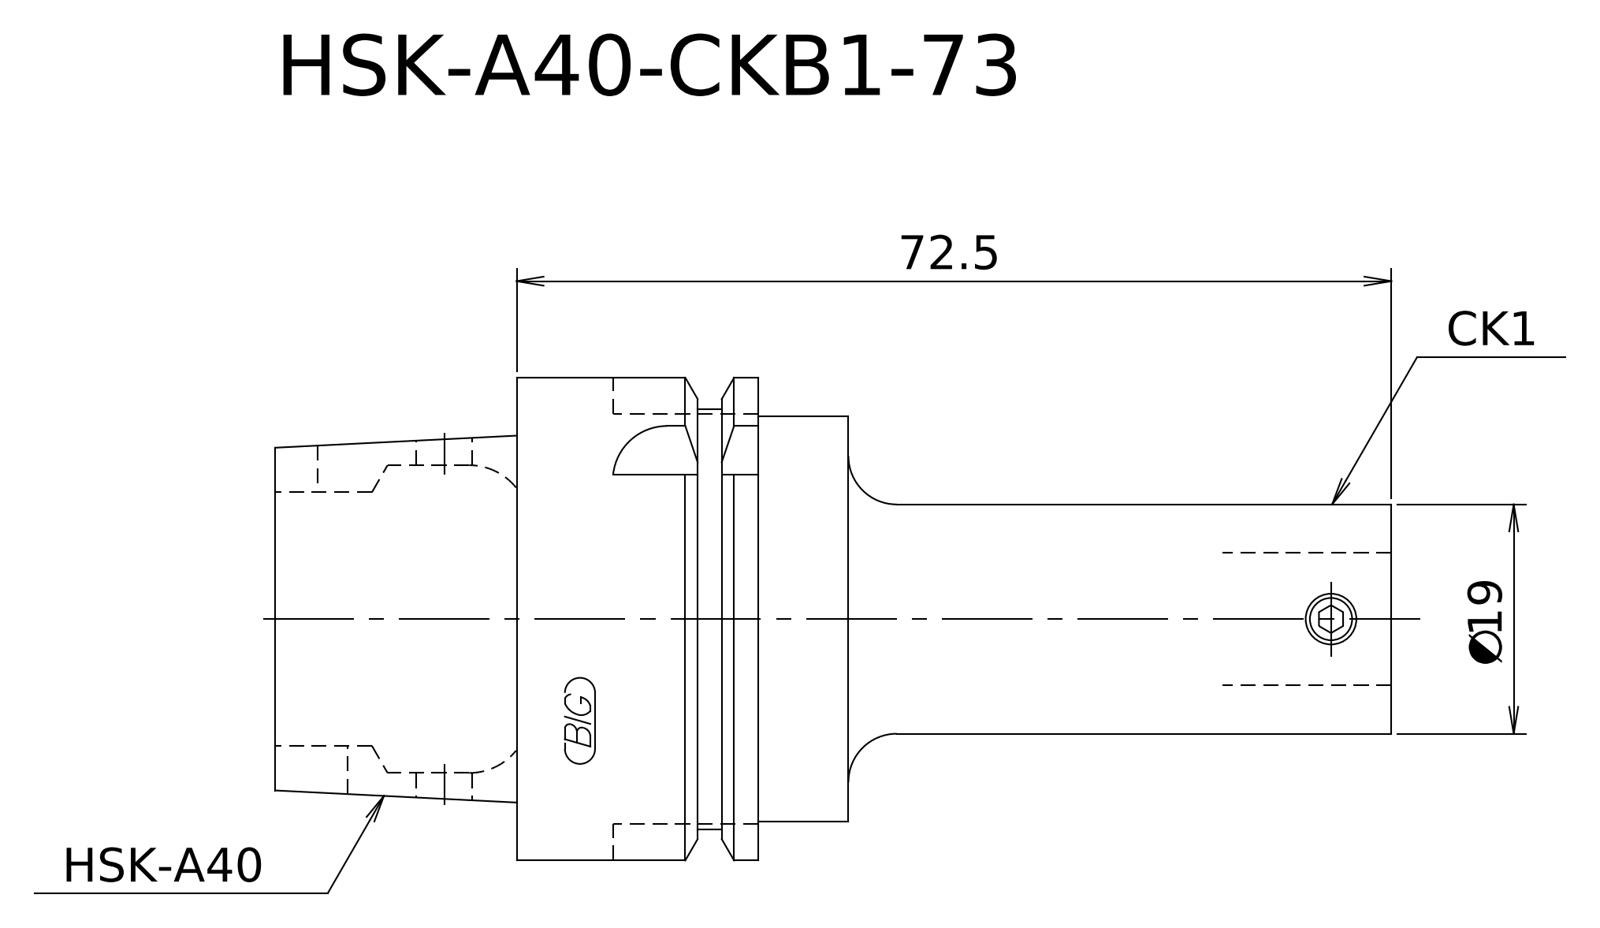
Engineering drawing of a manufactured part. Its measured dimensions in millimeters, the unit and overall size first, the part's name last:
Units: millimetres
Overall size (bounding box): 92.5 × 40 × 40
Round bosses / shafts (diameter × count): ⌀40 ×1, ⌀34.8 ×1, ⌀33.6 ×1, ⌀30.25 ×1, ⌀19 ×1
Main face-to-face distances: 20, 40, 7.5, 27.5, 47.5, 45, 52.5, 72.5, 92.5, 55.5
Volume: 57 768 mm³ · Surface area: 10 544 mm²
Bodies: 1 solid, 17 faces (7 planar, 6 cylindrical, 4 other)
STEP written by: Kubotek KeyCreator V8.5.1 (14335) (CONFIG_CONTROL_DESIGN)
